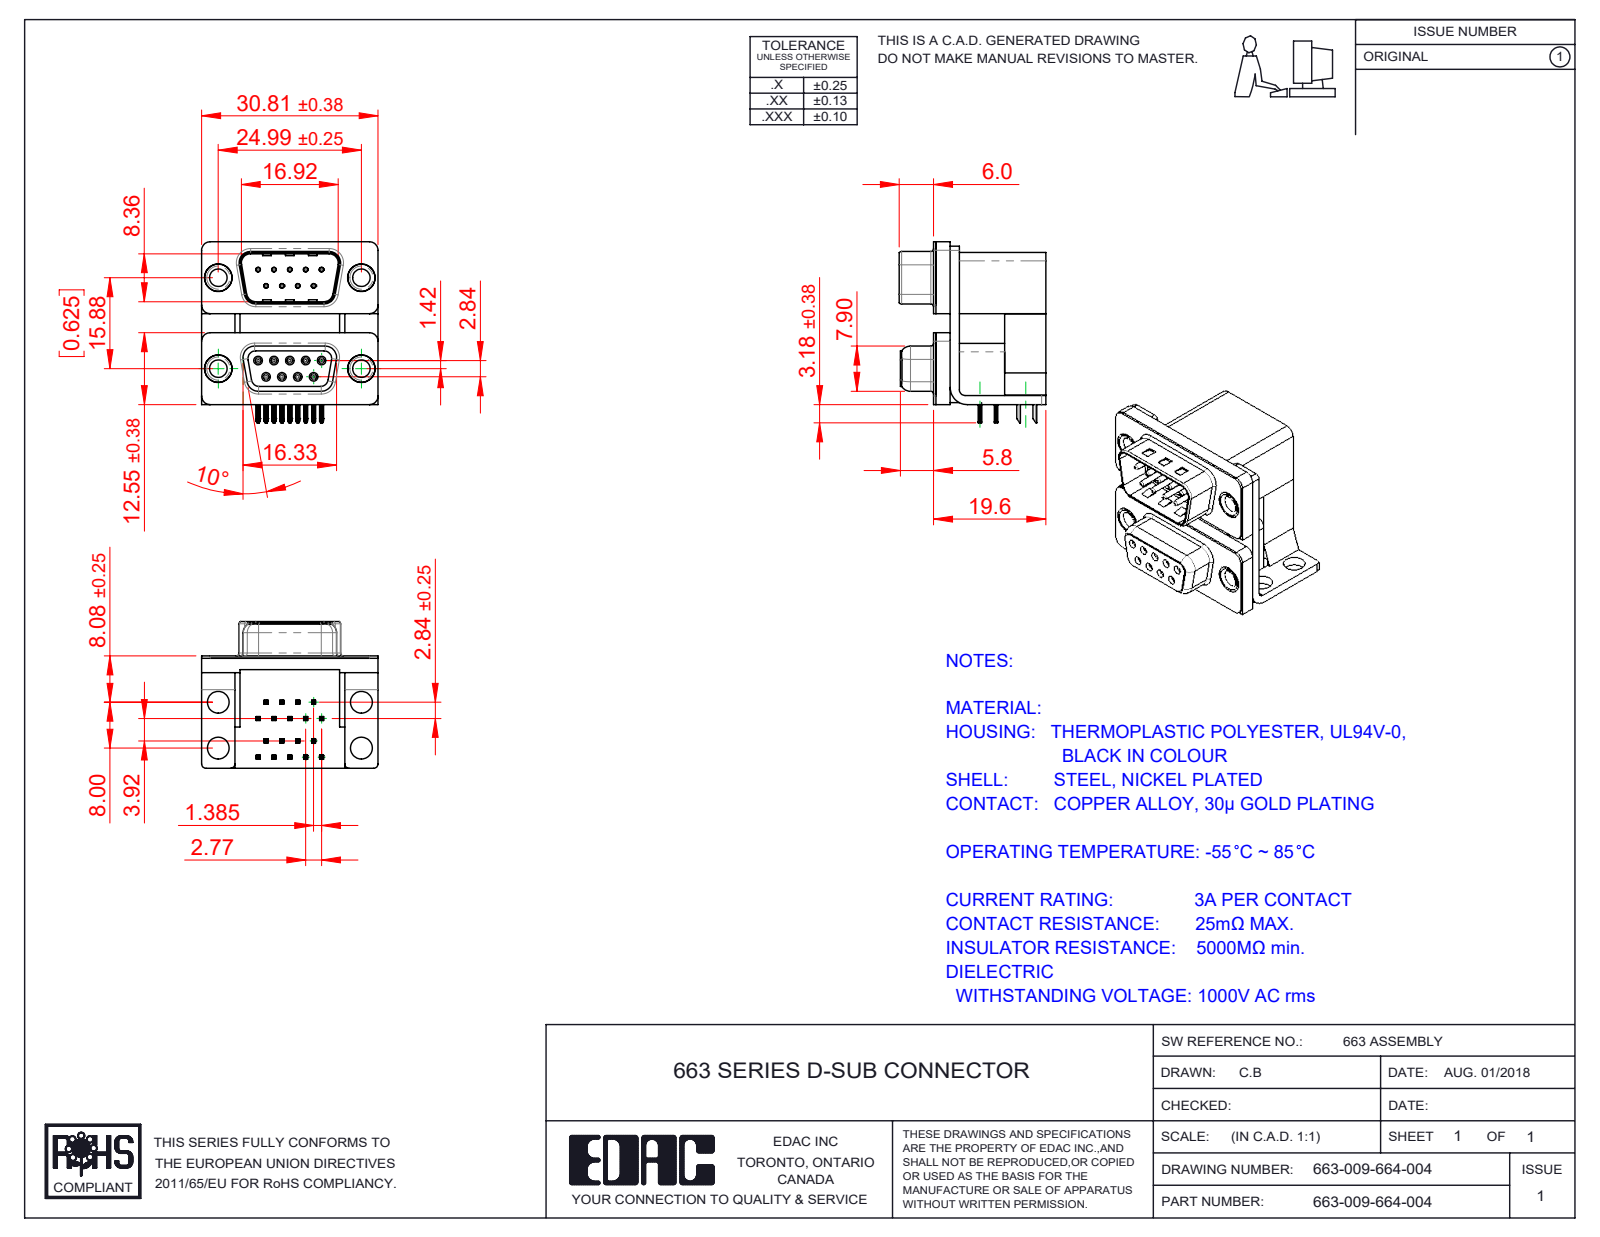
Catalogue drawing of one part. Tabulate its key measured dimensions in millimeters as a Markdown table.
| quantity | value |
| --- | --- |
| part name | 663 Housing Upper_09 Contacts L; 663 Thru Hole Rivet; 663 Mounting Bracket_NoneL; 663 Contact Bottom Upper_L (+8 more) |
| STEP written by | SolidWorks 2020 (CONFIG_CONTROL_DESIGN) |
| units | millimeters |
| bodies | 29 solids, 2445 faces (1263 planar, 659 cylindrical, 523 other) |
| overall size | 31.61 × 30.81 × 25.6 |
| volume | 10 317 mm³ |
| surface area | 11 978 mm² |
| round holes (diameter × count) | 0.8 × 18, 0.35 × 9, 0.9 × 9, 3.05 × 4, 3.5 × 4, 3.8 × 4, 4 × 4, 4.8 × 4, 5 × 4 |
| round bosses / shafts (diameter × count) | 1.2 × 9, 0.75 × 9, 4.9 × 4, 4.75 × 4, 3.85 × 4 |
| partial cylindrical surfaces (radius × count) | 0.1 × 72, 0.15 × 36, 0.25 × 36, 0.12 × 18, 0.35 × 18, 1.5 × 13, 0.5 × 12, 0.34 × 9 |
| main face-to-face distances | 0.4, 2.5, 16.7, 19.2, 19.6, 2.9, 1.6, 7.2, 9.5, 12 |
| hole center spacings | 3.16, 2.77, 16.12, 15.88, 5.54, 16.82, 13.11, 18.77 |
